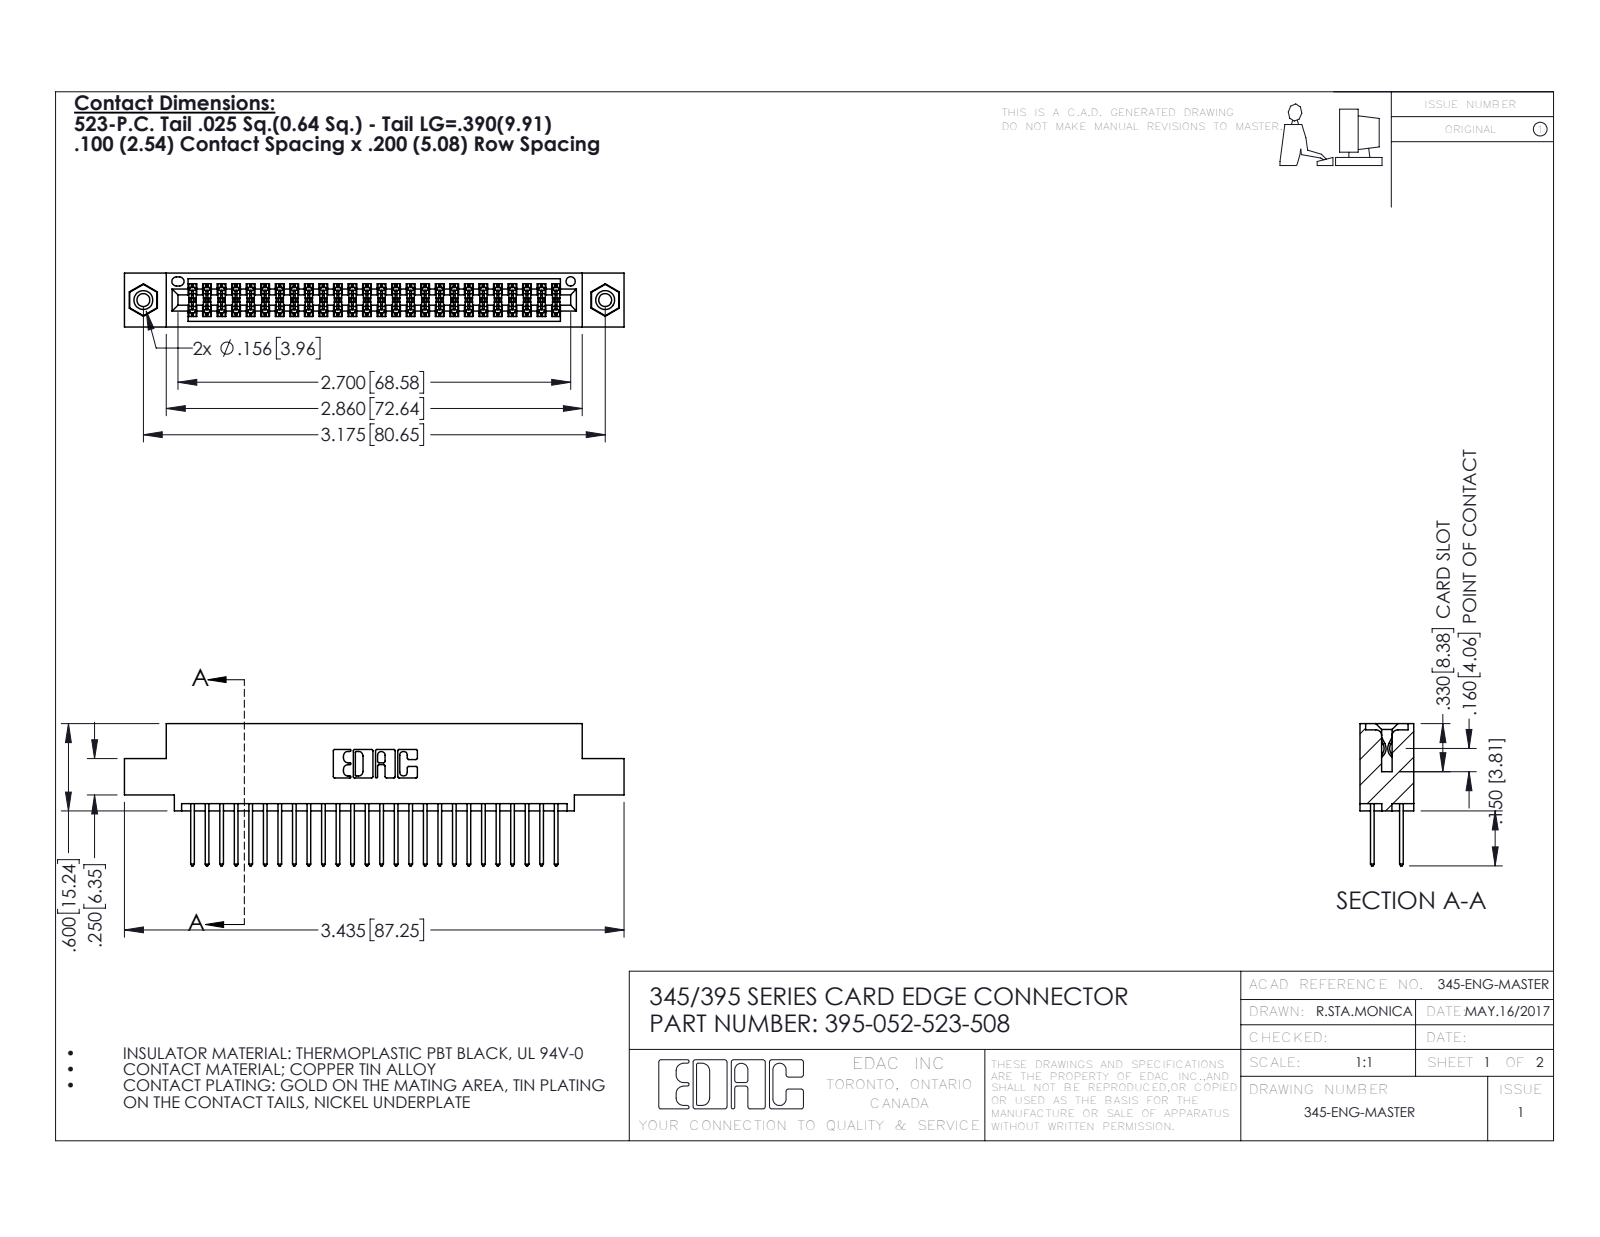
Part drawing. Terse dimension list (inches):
name: 345-250-001_345-250-003-102; 345 Part_0.110 Offset - 0.156 Dia-TI; 395-052-523-508; 345-292-001_345-293-123
written by: SolidWorks 2016 (CONFIG_CONTROL_DESIGN)
unit: in
bodies: 55 solids, 2790 faces (1832 planar, 942 cylindrical, 16 other)
size: 3.435 × 0.977 × 0.37
volume: 0.51 in³; area: 19.56 in²
holes: 2× ⌀0.089, 2× ⌀0.125, 2× ⌀0.156, 1× ⌀0.064
bosses: 2× ⌀0.155
rounds: 78× R0.006, 52× R0.01, 22× R0.01, 6× R0.007, 6× R0.031, 3× R0.026, 2× R0.014, 2× R0.019
face distances: 0.072, 0.298, 0.2, 0.098, 0.272, 0.025, 0.37, 0.225, 0.175, 0.149
hole spacings: 0.27, 2.94, 3.175
